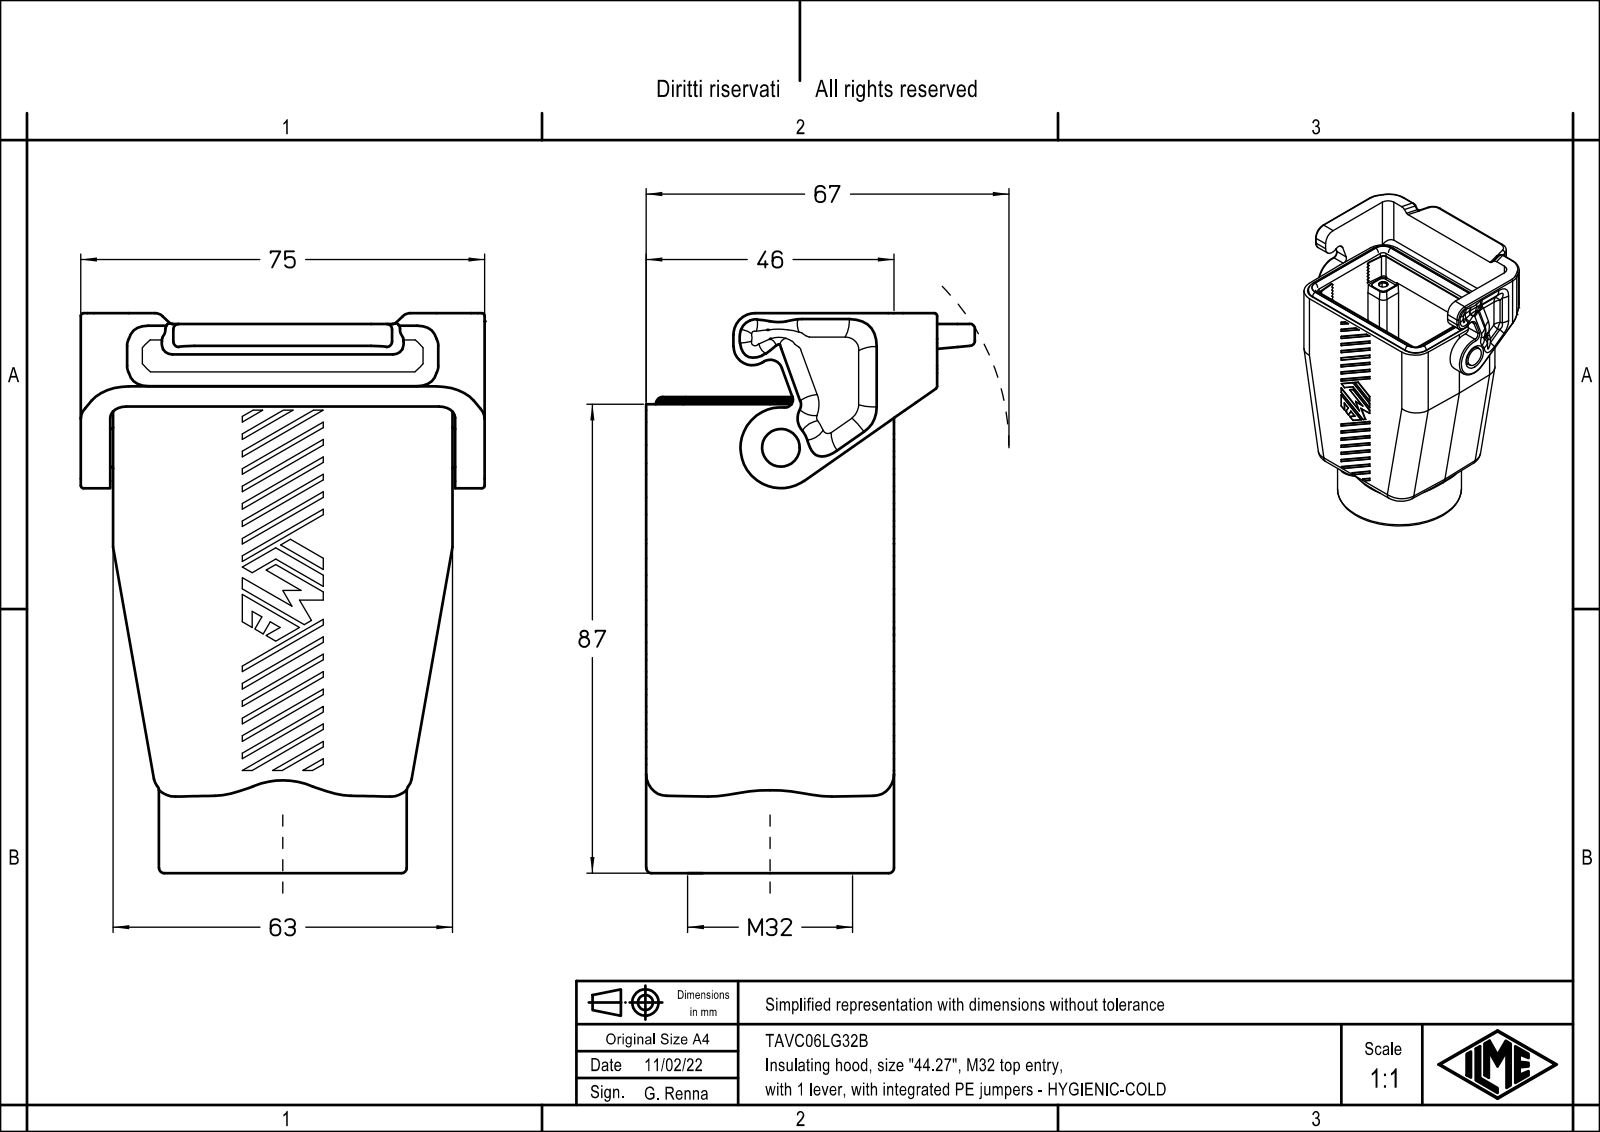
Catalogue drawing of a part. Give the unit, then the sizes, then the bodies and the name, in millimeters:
Units: millimetres
Overall size (bounding box): 103.9 × 75 × 61.15
Round holes (diameter × count): ⌀3.5 ×4, ⌀28 ×1, ⌀30.6 ×1
Round bosses / shafts (diameter × count): ⌀46 ×1, ⌀7 ×1
Partial cylindrical surfaces — rounded edges, fillets, slot ends (radius × count): R0.15 ×128, R1.5 ×15, R2 ×14, R3 ×13, R1.3 ×12, R1 ×8, R7 ×8, R1.6 ×4
Main face-to-face distances: 5.4, 40.6, 46, 35.2, 3, 8.4, 49, 43.6, 5.8, 6.1
Hole centre spacings: 25.81, 27, 44, 51.62
Volume: 110 976 mm³ · Surface area: 43 047 mm²
Bodies: 1 solid, 708 faces (312 planar, 344 cylindrical, 52 other)
Part name (STEP PRODUCT): TAVH 06 LG32
STEP written by: Creo Elements/Direct Modeling 20.1B 02-Apr-2019 (C) Parametric Technology GmbH (AUTOMOTIVE_DESIGN)
